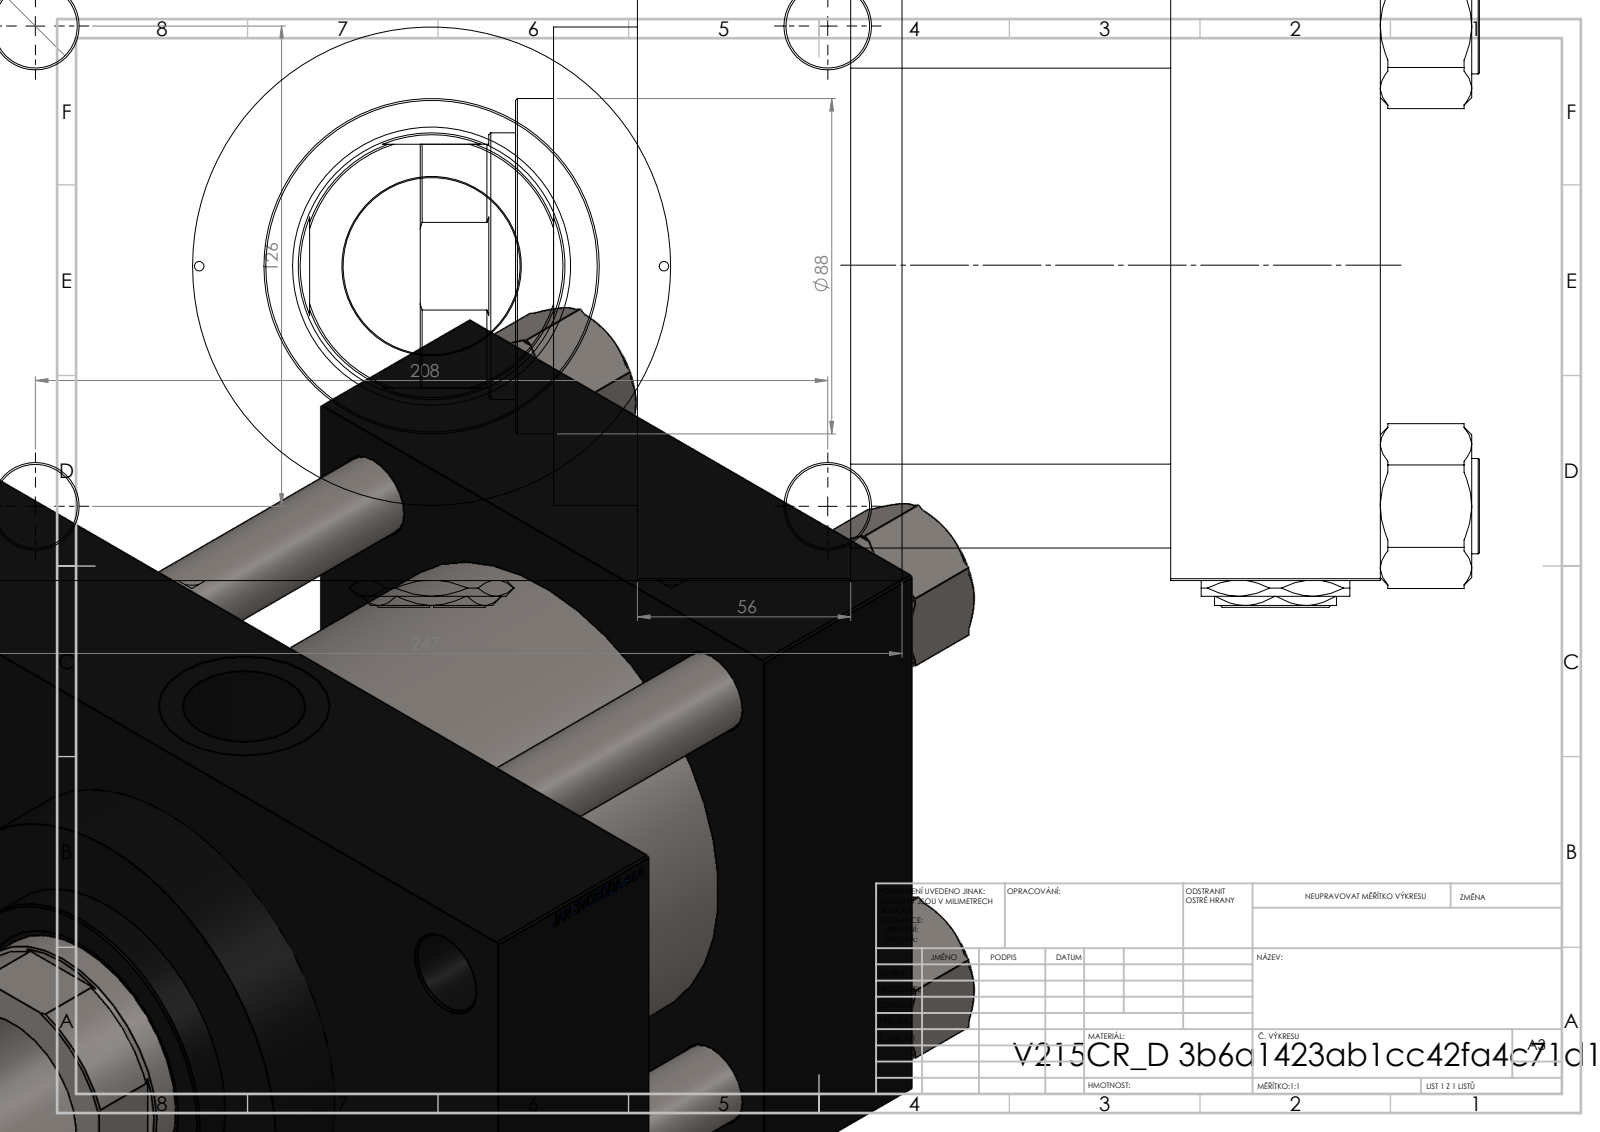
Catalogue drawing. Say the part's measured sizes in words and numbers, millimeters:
The part is named "V215CR_D_Body; NUT_M5_D; V215CR_VCP_D; V215CR_D_TYCINKA (+2 more)". Its 3-D file was written by "SolidWorks 2019 (CONFIG_CONTROL_DESIGN)". It is 12 solids with 1197 faces: 568 planar, 91 cylindrical and 538 other. Overall it measures 278 by 247 by 174.07 millimeters. Its volume is 5 054 000 cubic millimeters and its surface area 541 418 square millimeters. Round holes: 8 of diameter 22, 2 of diameter 2.5, 2 of diameter 7, 2 of diameter 32.24, 2 of diameter 45, 1 of diameter 46.5, 1 of diameter 70, 1 of diameter 73, 1 of diameter 96, 1 of diameter 125, 1 of diameter 125.5. Round bosses or shafts: 4 of diameter 25, 1 of diameter 131, 1 of diameter 88. Partial cylindrical surfaces (rounded edges, fillets, slot ends): 1 of radius 34. The main face-to-face distances are 165, 84, 55, 139, 56, 195, 140, 41, 206, 173.74. The hole center spacings are 41.05, 62.98, 76.28, 89.02, 121.59, 125.9, 132.47, 139.02.
